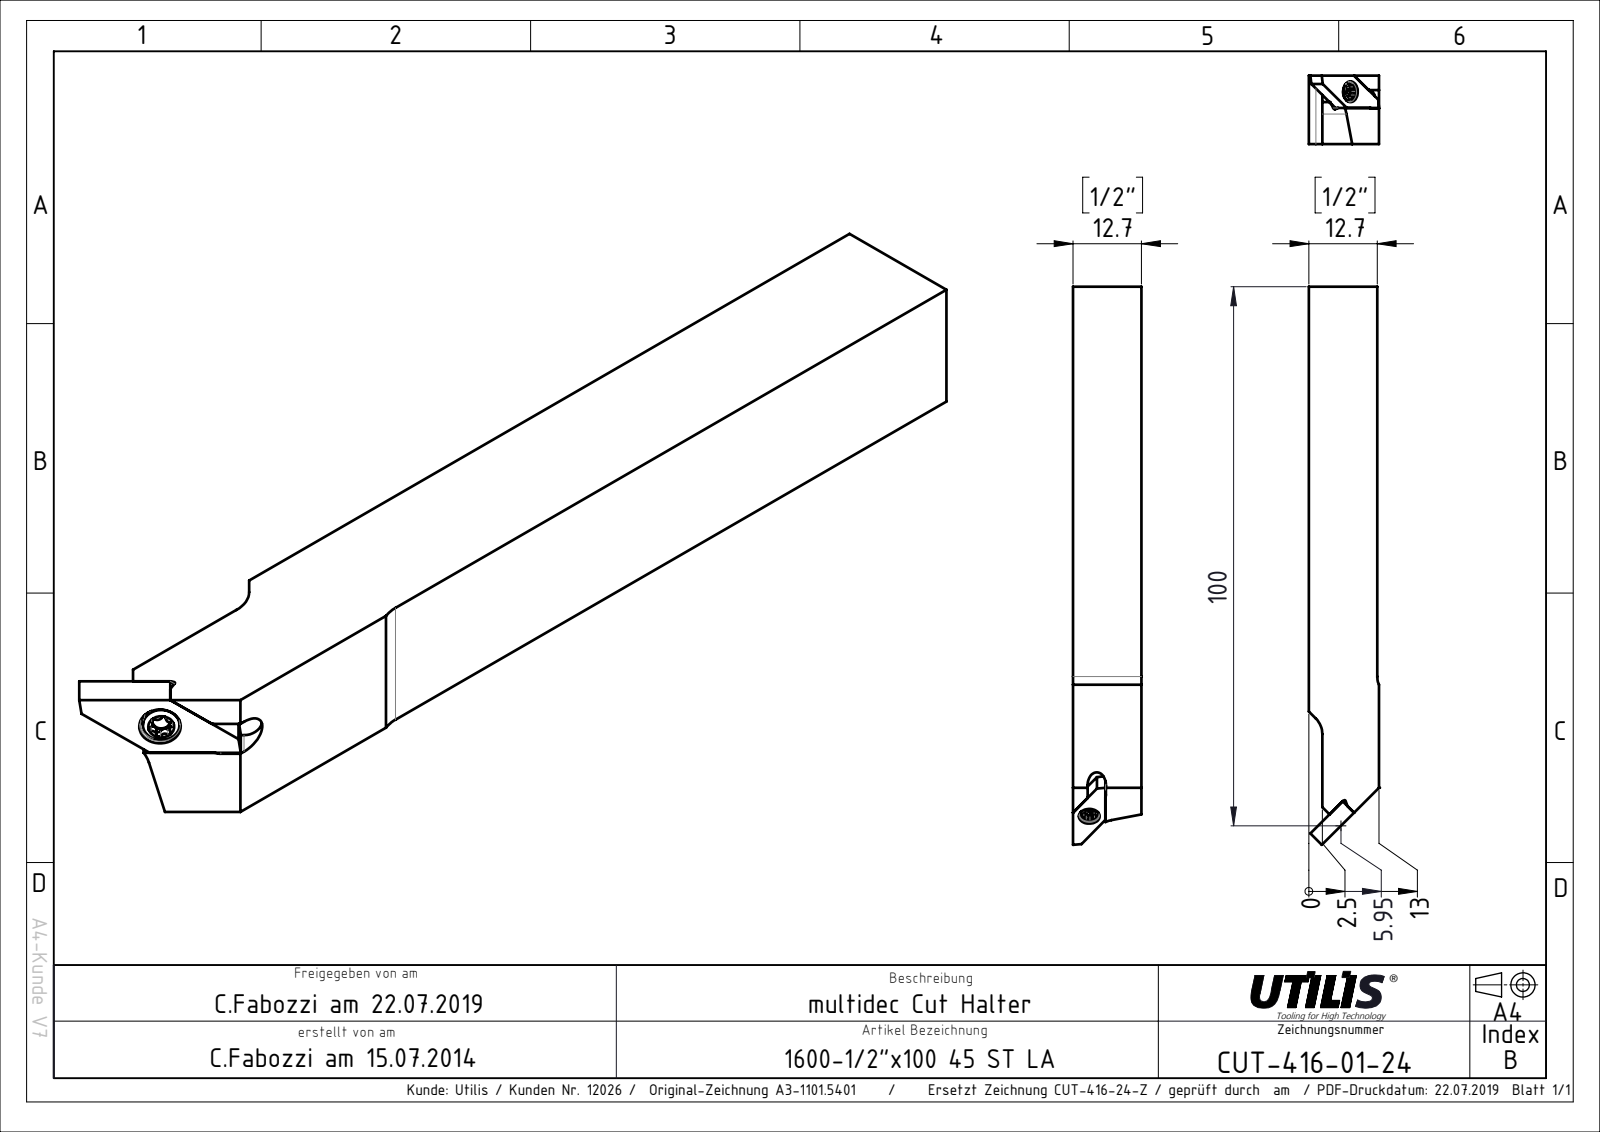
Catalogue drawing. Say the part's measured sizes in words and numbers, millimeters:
The part is named "CUT-416_24; CUT-Vorlage 1600_1600 Vorlage; CUT-416-01-24". Its 3-D file was written by "SolidWorks 2020 (AUTOMOTIVE_DESIGN)". It is 2 solids with 41 faces: 26 planar, 8 cylindrical and 7 other. Overall it measures 103.54 by 13.02 by 12.7 millimeters. Its volume is 15 123 cubic millimeters and its surface area 5 393 square millimeters. Round holes: 1 of diameter 2.9, 1 of diameter 3.1. Partial cylindrical surfaces (rounded edges, fillets, slot ends): 3 of radius 4.1, 1 of radius 0.5, 1 of radius 1.55, 1 of radius 1.7. The main face-to-face distances are 12.7, 13, 10.5, 10.2, 2.5, 3, 6.7, 6, 6.01, 10.78.
